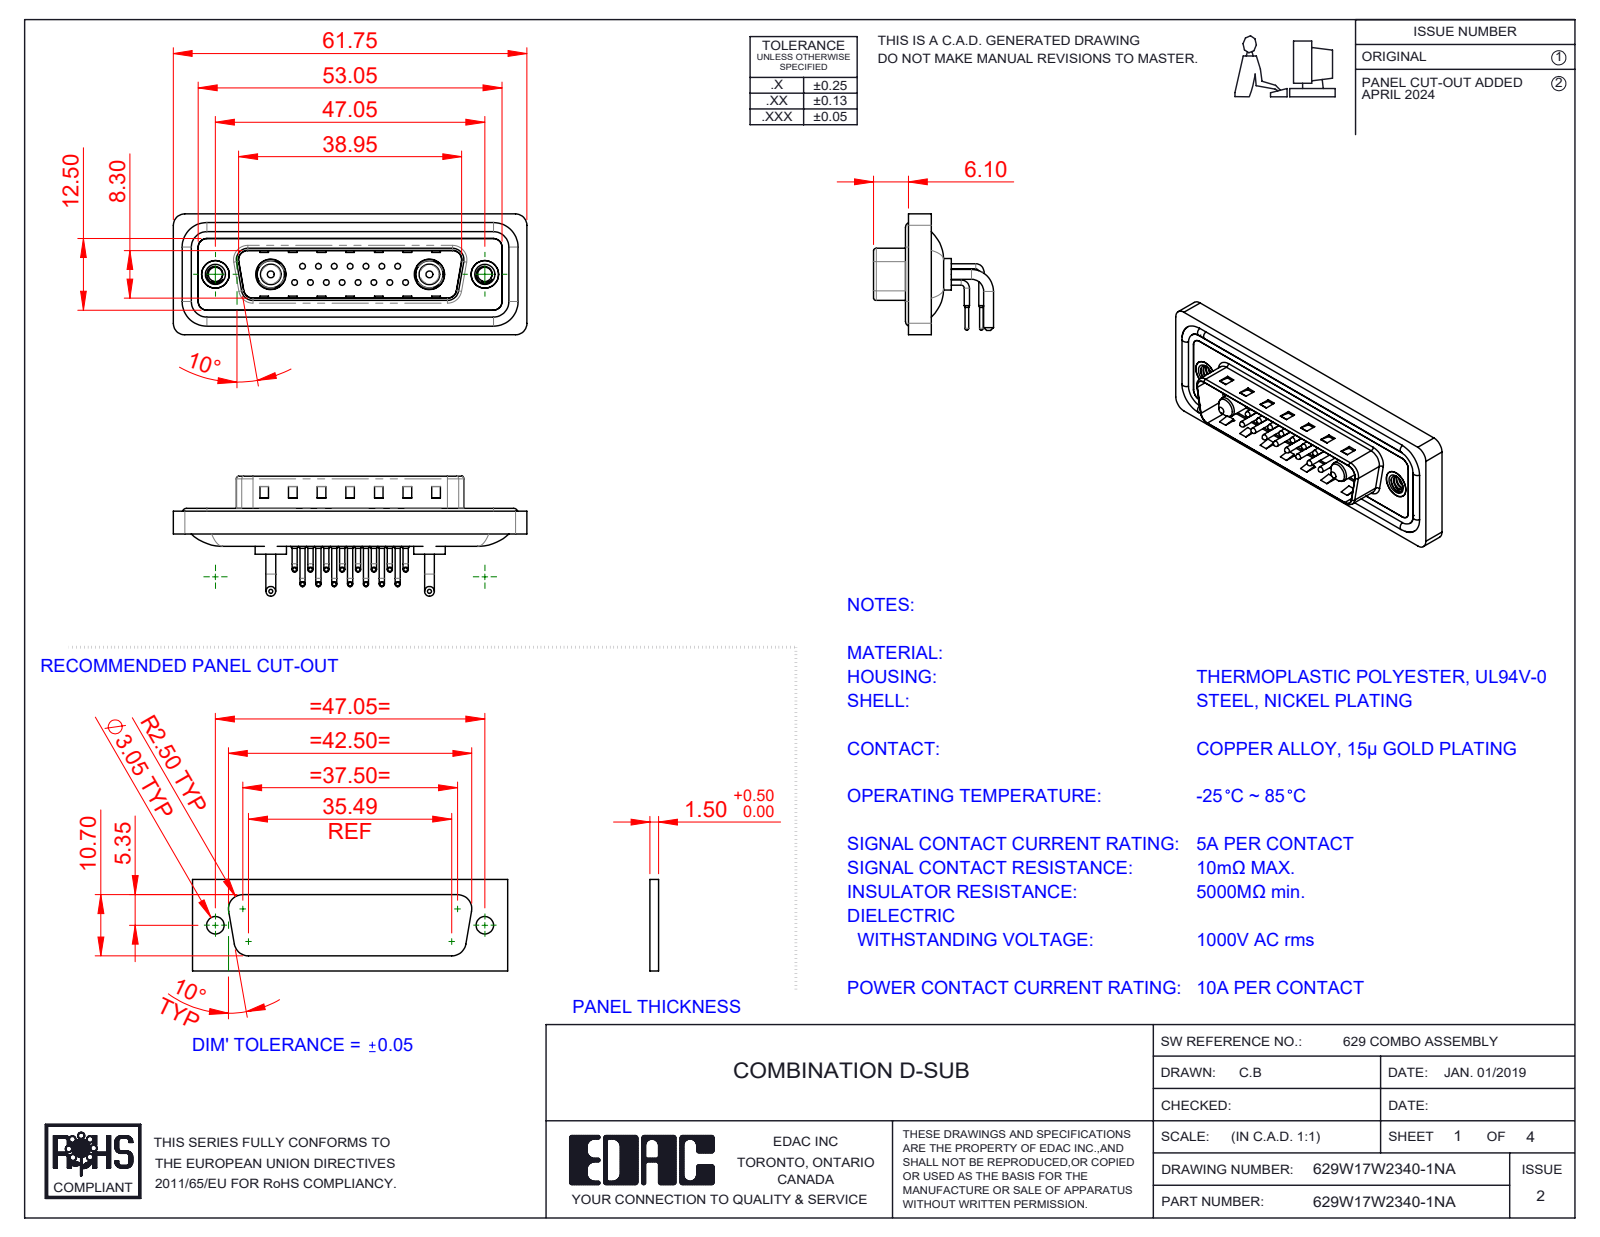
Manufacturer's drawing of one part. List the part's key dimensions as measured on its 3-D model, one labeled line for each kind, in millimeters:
Part name (STEP PRODUCT): 629W17W2340-1NA; 629Combo Waterproof Housing_25 Contacts; 629Combo Housing_17W2; 629Combo Contact Row 1 (+5 more)
STEP written by: SolidWorks 2023 (CONFIG_CONTROL_DESIGN)
Units: millimetres
Bodies: 26 solids, 2213 faces (1189 planar, 768 cylindrical, 256 other)
Overall size (bounding box): 61.75 × 21.1 × 20.95
Volume: 7 400 mm³ · Surface area: 12 503 mm²
Round holes (diameter × count): ⌀0.75 ×15, ⌀1.6 ×15, ⌀2 ×15, ⌀2.5 ×2, ⌀4 ×2, ⌀4.8 ×2, ⌀4.85 ×2, ⌀5 ×2, ⌀5.3 ×2
Round bosses / shafts (diameter × count): ⌀0.9 ×30, ⌀1.5 ×15, ⌀1 ×15, ⌀0.65 ×15, ⌀1.7 ×4, ⌀1.6 ×4, ⌀5.5 ×2, ⌀5.2 ×2
Partial cylindrical surfaces — rounded edges, fillets, slot ends (radius × count): R1.5 ×18, R2 ×18, R1.01 ×15, R0.5 ×8, R1.6 ×8, R0.25 ×4, R0.6 ×4, R0.65 ×4
Main face-to-face distances: 0.4, 2.9, 0.8, 4.1, 1.1, 2.1, 1.6, 4.5, 1.5, 2.5
Hole centre spacings: 3.16, 2.77, 5.54, 8.31, 5.04, 7.49, 11.08, 5.03
